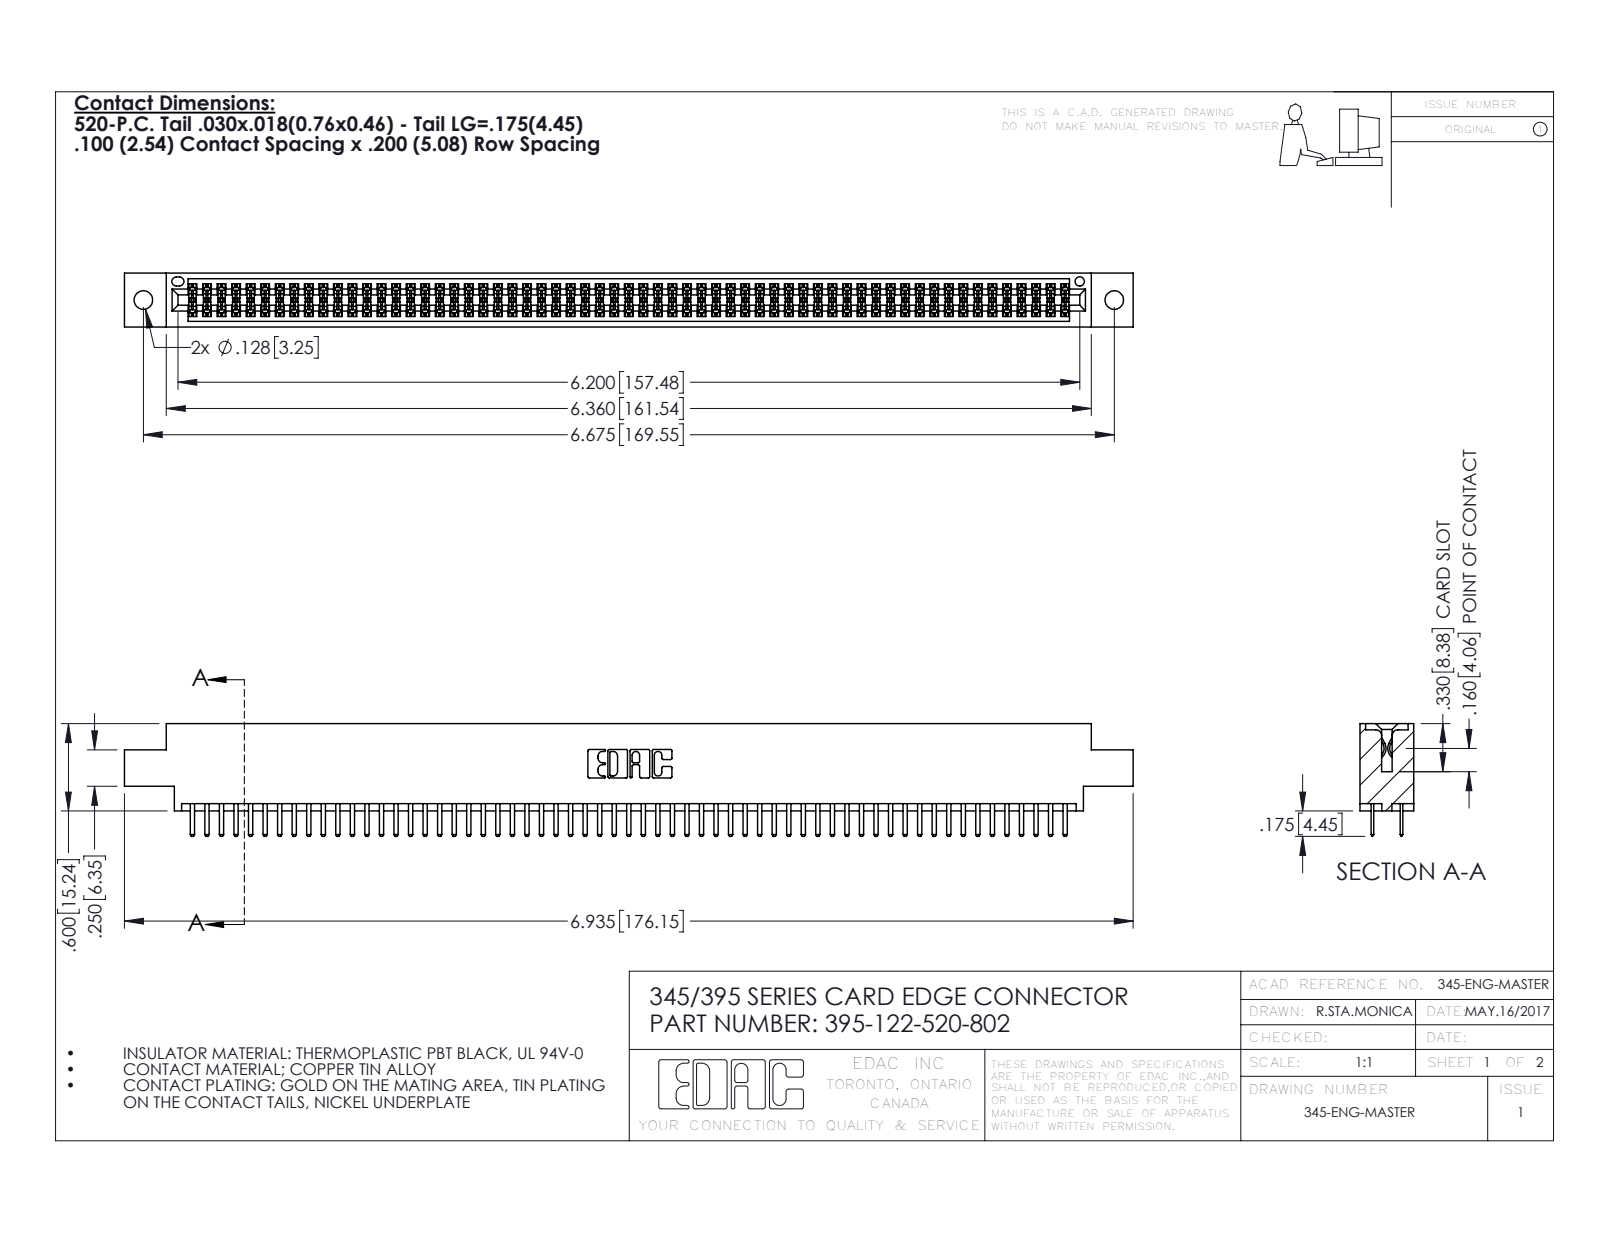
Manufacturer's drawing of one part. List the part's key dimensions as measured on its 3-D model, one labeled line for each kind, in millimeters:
Part name (STEP PRODUCT): 345-292-001_345-293-120; 345 Part_0.170 Offset - 0.128 Dia; 395-122-520-802
STEP written by: SolidWorks 2016 (CONFIG_CONTROL_DESIGN)
Units: millimetres
Bodies: 123 solids, 6718 faces (4354 planar, 2364 cylindrical, 0 other)
Overall size (bounding box): 176.1 × 19.7 × 9.4
Volume: 17 090 mm³ · Surface area: 25 380 mm²
Round holes (diameter × count): ⌀3.3 ×2, ⌀1.6 ×1
Partial cylindrical surfaces — rounded edges, fillets, slot ends (radius × count): R0.2 ×183, R0.3 ×126, R0.3 ×22, R0.2 ×6, R0.8 ×6, R0.7 ×3, R0.4 ×2, R0.5 ×2
Main face-to-face distances: 7.6, 1.8, 5.1, 9.4, 2.5, 6.9, 0.6, 5.7, 0.6, 1.8
Hole centre spacings: 6.9, 163.6, 169.5
